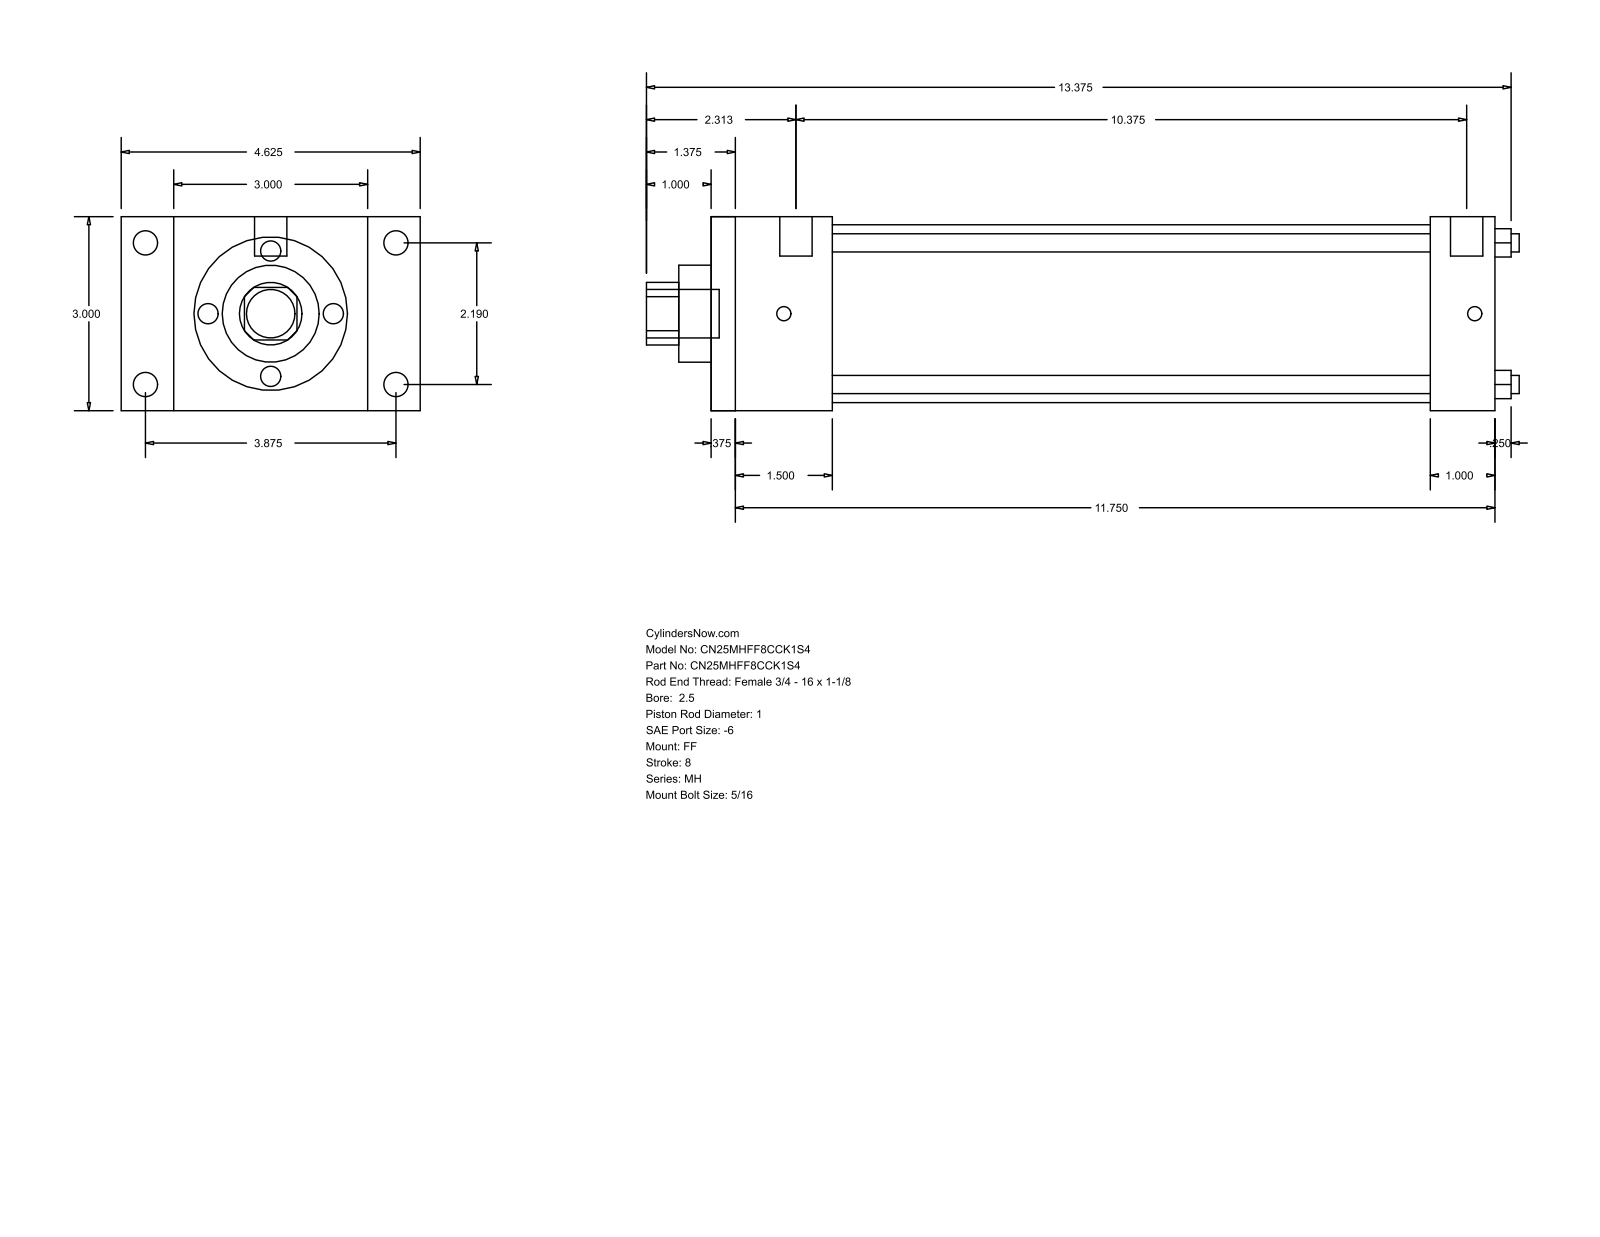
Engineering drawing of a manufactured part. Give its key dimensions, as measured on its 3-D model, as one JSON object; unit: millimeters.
{"part_name": "MH_FF__0250_1", "step_written_by": "GSSL Pune (CONFIG_CONTROL_DESIGN)", "units": "millimeters", "bodies": {"solids": 0, "faces": 92, "planar": 64, "cylindrical": 28, "other": 0}, "overall_size": [342.9, 117.47, 76.2], "round_holes": [[7.14, 4], [25.4, 1], [38.1, 1], [69.85, 1]], "round_bosses_or_shafts": [[9.53, 4], [5.56, 4], [12.7, 2], [19.05, 1]], "partial_cylinders_radius": [[12.29, 1]], "face_to_face_distances": [76.2, 307.98, 9.52, 298.46, 25.4, 47.63, 282.58, 38.11, 273.06, 234.95], "hole_center_spacings": [39.33, 55.62, 78.66]}
